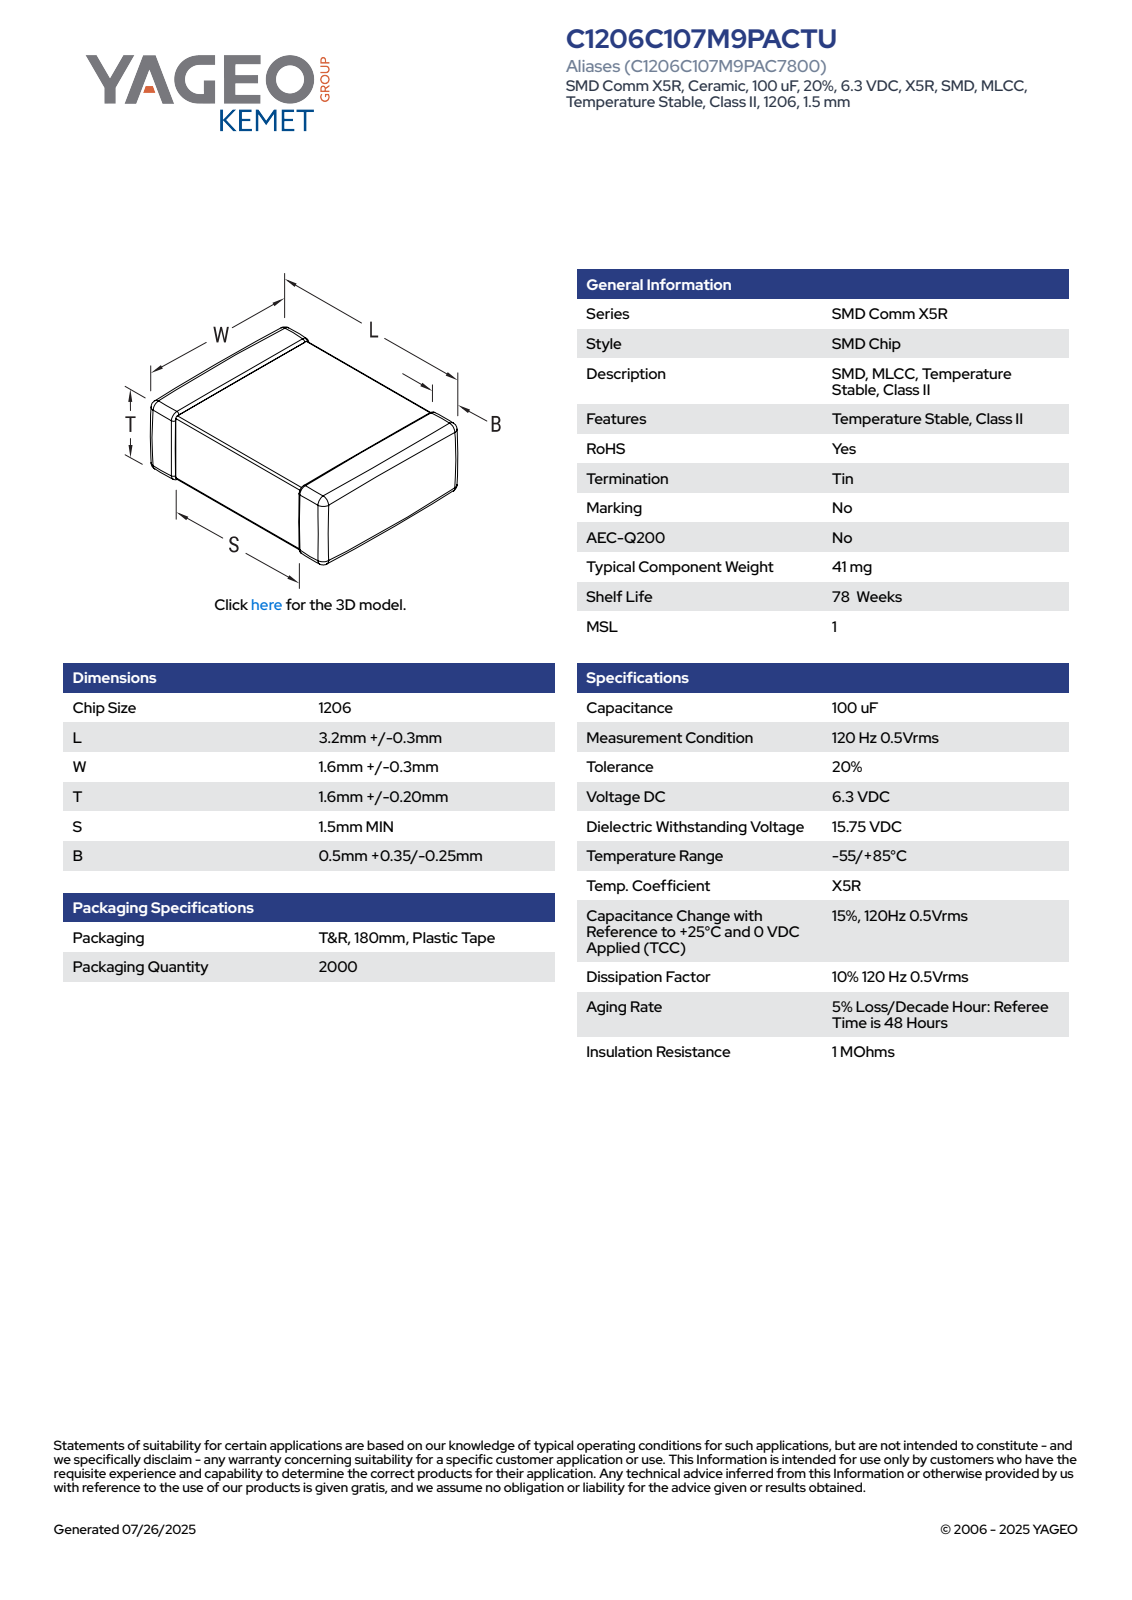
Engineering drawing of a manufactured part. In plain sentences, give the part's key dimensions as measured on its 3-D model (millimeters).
The part is named "CCS_CCSTDNOS_1206_L3.5W1.9T1.8B0.85". Its 3-D file was written by "SolidWorks 2014 (AUTOMOTIVE_DESIGN)". It is 4 solids with 125 faces: 71 planar, 38 cylindrical and 16 other. Overall it measures 3.5 by 1.9 by 1.8 millimeters. Its volume is 11 cubic millimeters and its surface area 32 square millimeters. The main face-to-face distances are 1.76, 1.86, 1.72, 3.5, 1.82, 1.8, 1.9, 1.77, 1.73, 1.02.
